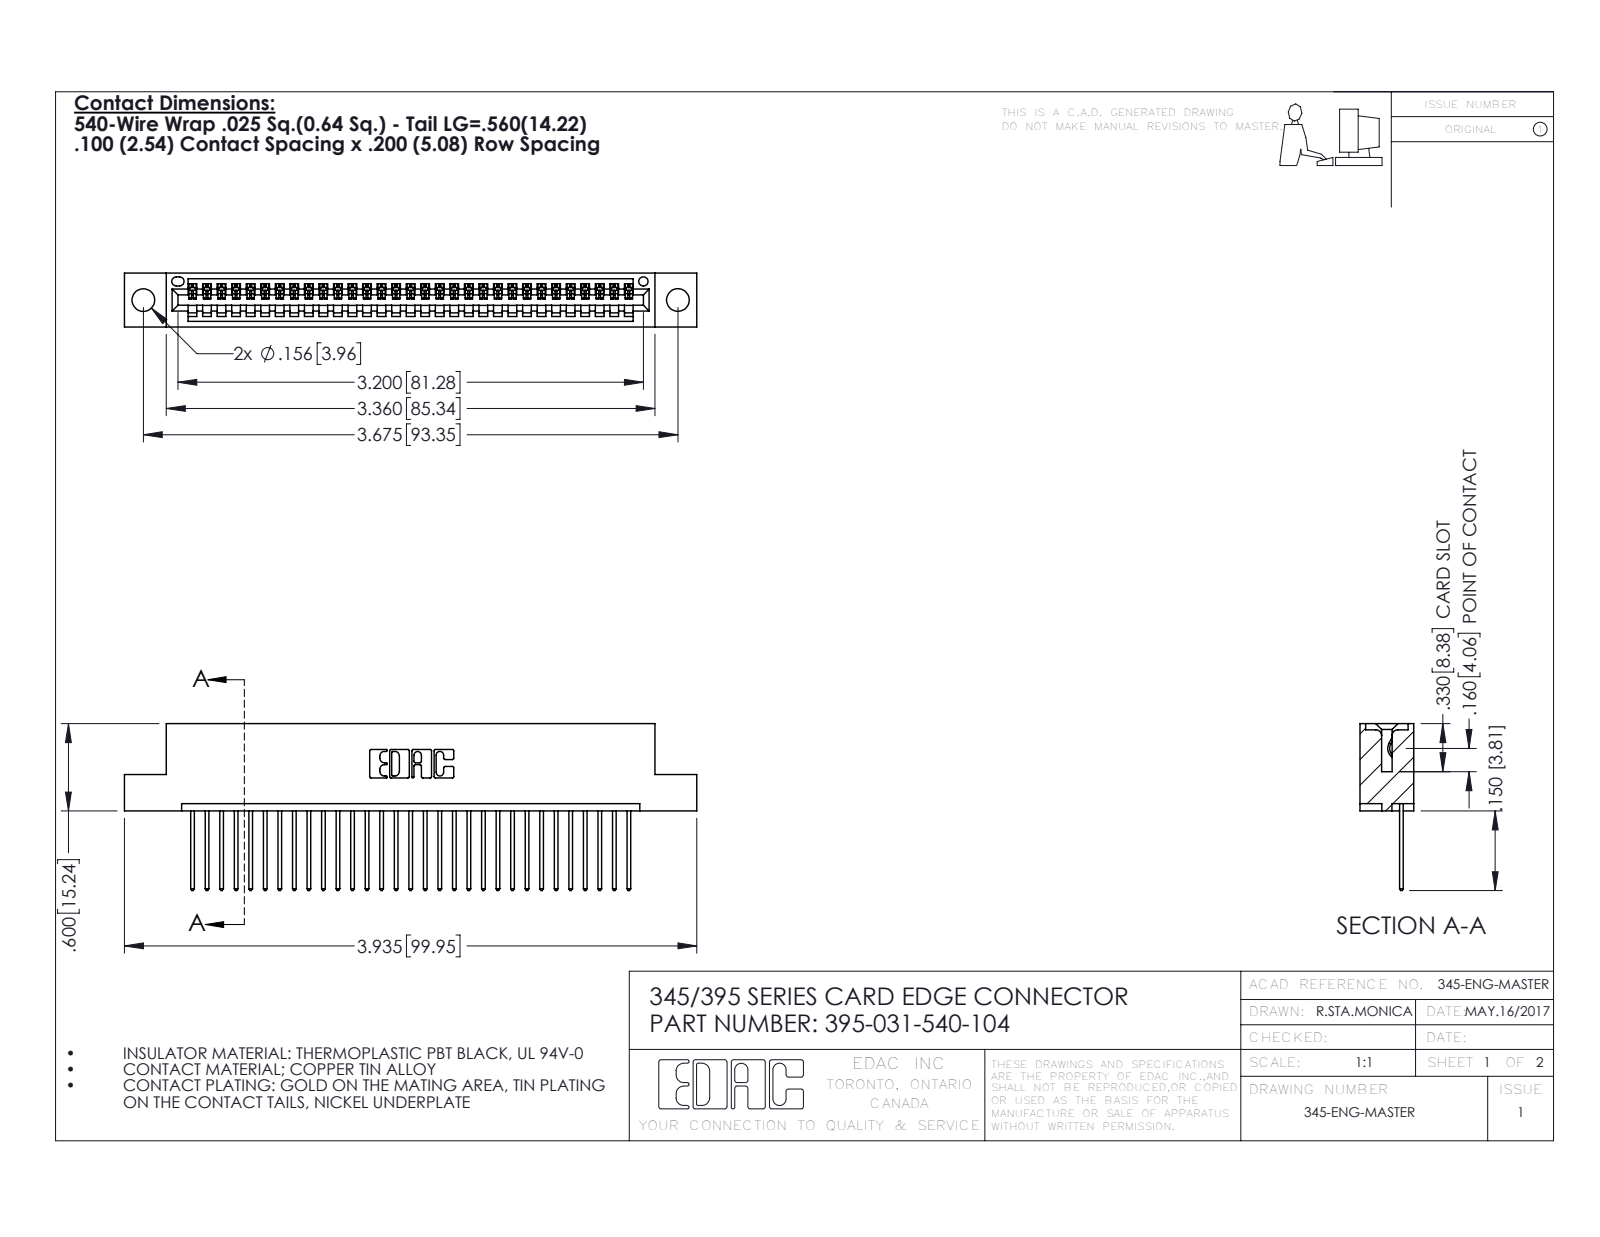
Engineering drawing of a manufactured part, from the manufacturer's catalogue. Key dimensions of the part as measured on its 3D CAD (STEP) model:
Part name (STEP PRODUCT): 345-292-001_345-293-140; 395-031-540-104; 345 Part_Flush Mounting Lugs - 0.156 Dia-TH
STEP written by: SolidWorks 2016 (CONFIG_CONTROL_DESIGN)
Units: inches
Bodies: 32 solids, 1924 faces (1320 planar, 604 cylindrical, 0 other)
Overall size (bounding box): 3.935 × 1.147 × 0.37
Volume: 0.571 in³ · Surface area: 19.21 in²
Round holes (diameter × count): ⌀0.156 ×2, ⌀0.064 ×1
Partial cylindrical surfaces — rounded edges, fillets, slot ends (radius × count): R0.006 ×62, R0.01 ×62, R0.01 ×22, R0.007 ×6, R0.031 ×6, R0.026 ×3, R0.031 ×2, R0.04 ×2
Main face-to-face distances: 0.298, 0.072, 0.2, 0.37, 0.098, 0.272, 0.025, 0.225, 0.149, 0.072
Hole centre spacings: 0.27, 3.44, 3.675
